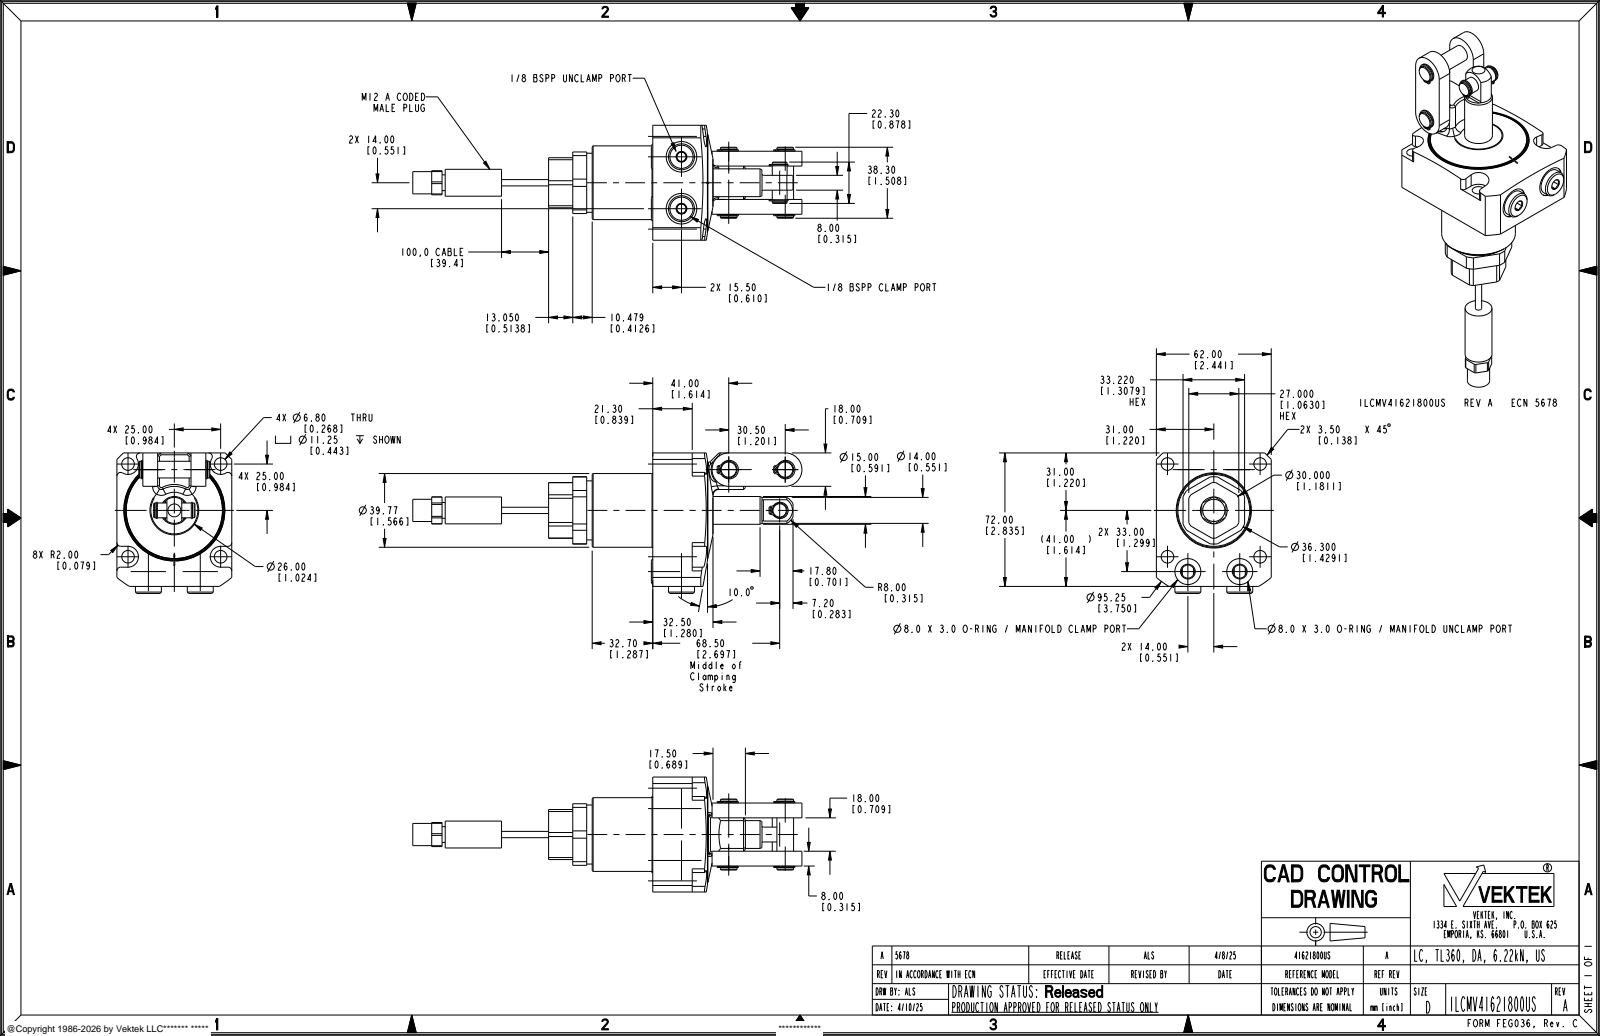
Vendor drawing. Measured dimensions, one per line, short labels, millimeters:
name: ILCMV41621800_BODY_US; ILCMV41621800_LUG_US; ILCMV41621800US
written by: CREO PARAMETRIC BY PTC INC, 2021164 (AUTOMOTIVE_DESIGN)
unit: mm
bodies: 4 solids, 455 faces (168 planar, 201 cylindrical, 86 other)
size: 210.03 × 75.81 × 62
volume: 217 194 mm³; area: 47 209 mm²
holes: 6× ⌀1.04, 4× ⌀6.8, 2× ⌀5, 2× ⌀7.04, 2× ⌀8.84, 2× ⌀14, 2× ⌀16.5, 1× ⌀52.03
bosses: 3× ⌀8, 2× ⌀14, 2× ⌀9.99, 2× ⌀9.73, 2× ⌀9, 2× ⌀8.38, 2× ⌀8.25, 1× ⌀51.93
rounds: 10× R2, 6× R1.04, 4× R0.8, 4× R1.76, 4× R5.62, 2× R2.32, 2× R9, 1× R4.38
face distances: 20, 62, 14, 48, 8, 22, 40, 26, 18, 17.5
hole spacings: 35.36, 50, 2.34, 13.6, 22.14, 28, 30.5, 30.59
